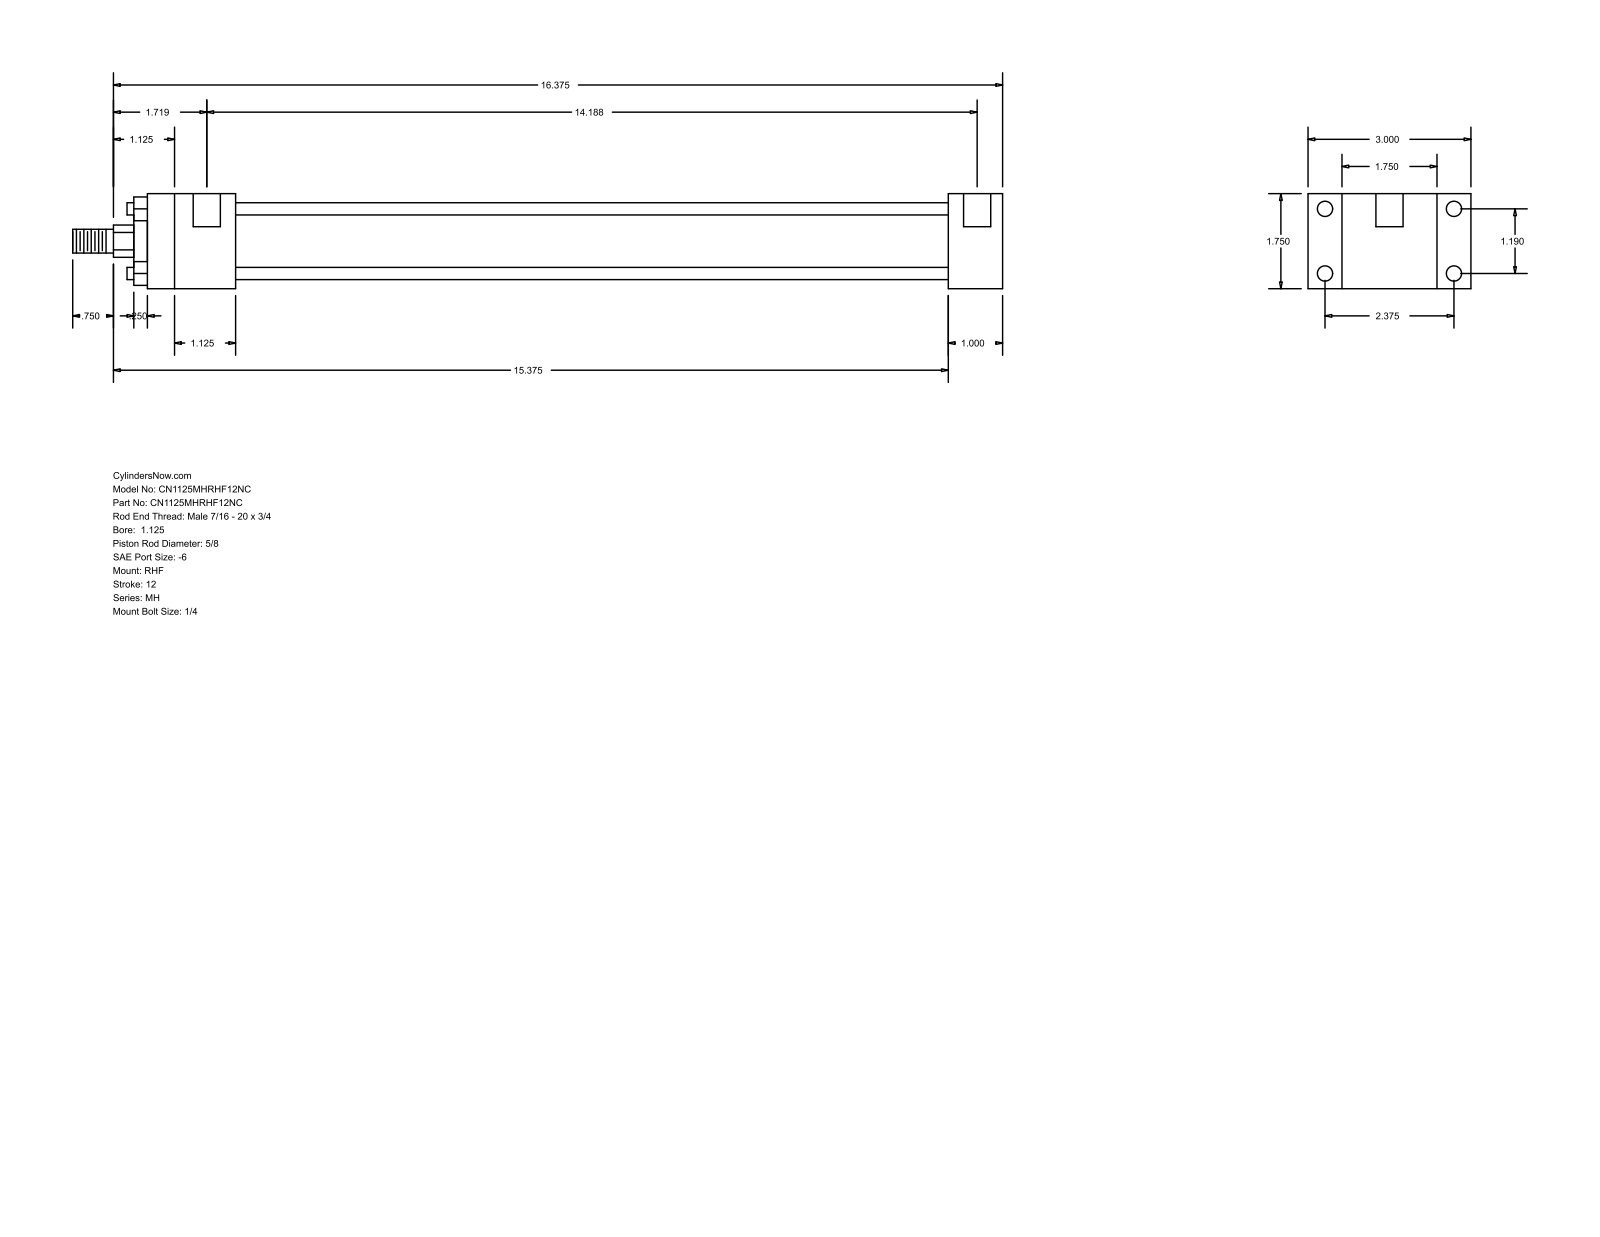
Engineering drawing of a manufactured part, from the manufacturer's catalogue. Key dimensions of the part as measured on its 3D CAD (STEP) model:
Part name (STEP PRODUCT): MH_RHF__0112_0.625
STEP written by: GSSL Pune (CONFIG_CONTROL_DESIGN)
Units: millimetres
Bodies: 0 solids, 88 faces (60 planar, 28 cylindrical, 0 other)
Overall size (bounding box): 434.98 × 76.2 × 44.45
Round holes (diameter × count): ⌀5.56 ×4, ⌀7.14 ×4, ⌀12.7 ×2
Round bosses / shafts (diameter × count): ⌀5.71 ×4, ⌀34.92 ×1, ⌀28.57 ×1, ⌀15.88 ×1, ⌀11.11 ×1
Partial cylindrical surfaces — rounded edges, fillets, slot ends (radius × count): R7.54 ×1
Main face-to-face distances: 44.46, 15.87, 60.33, 25.41, 76.2, 333.37, 358.78, 41.27, 374.64, 400.05
Hole centre spacings: 30.22, 60.32, 67.47, 357.19, 3.17, 360.36
